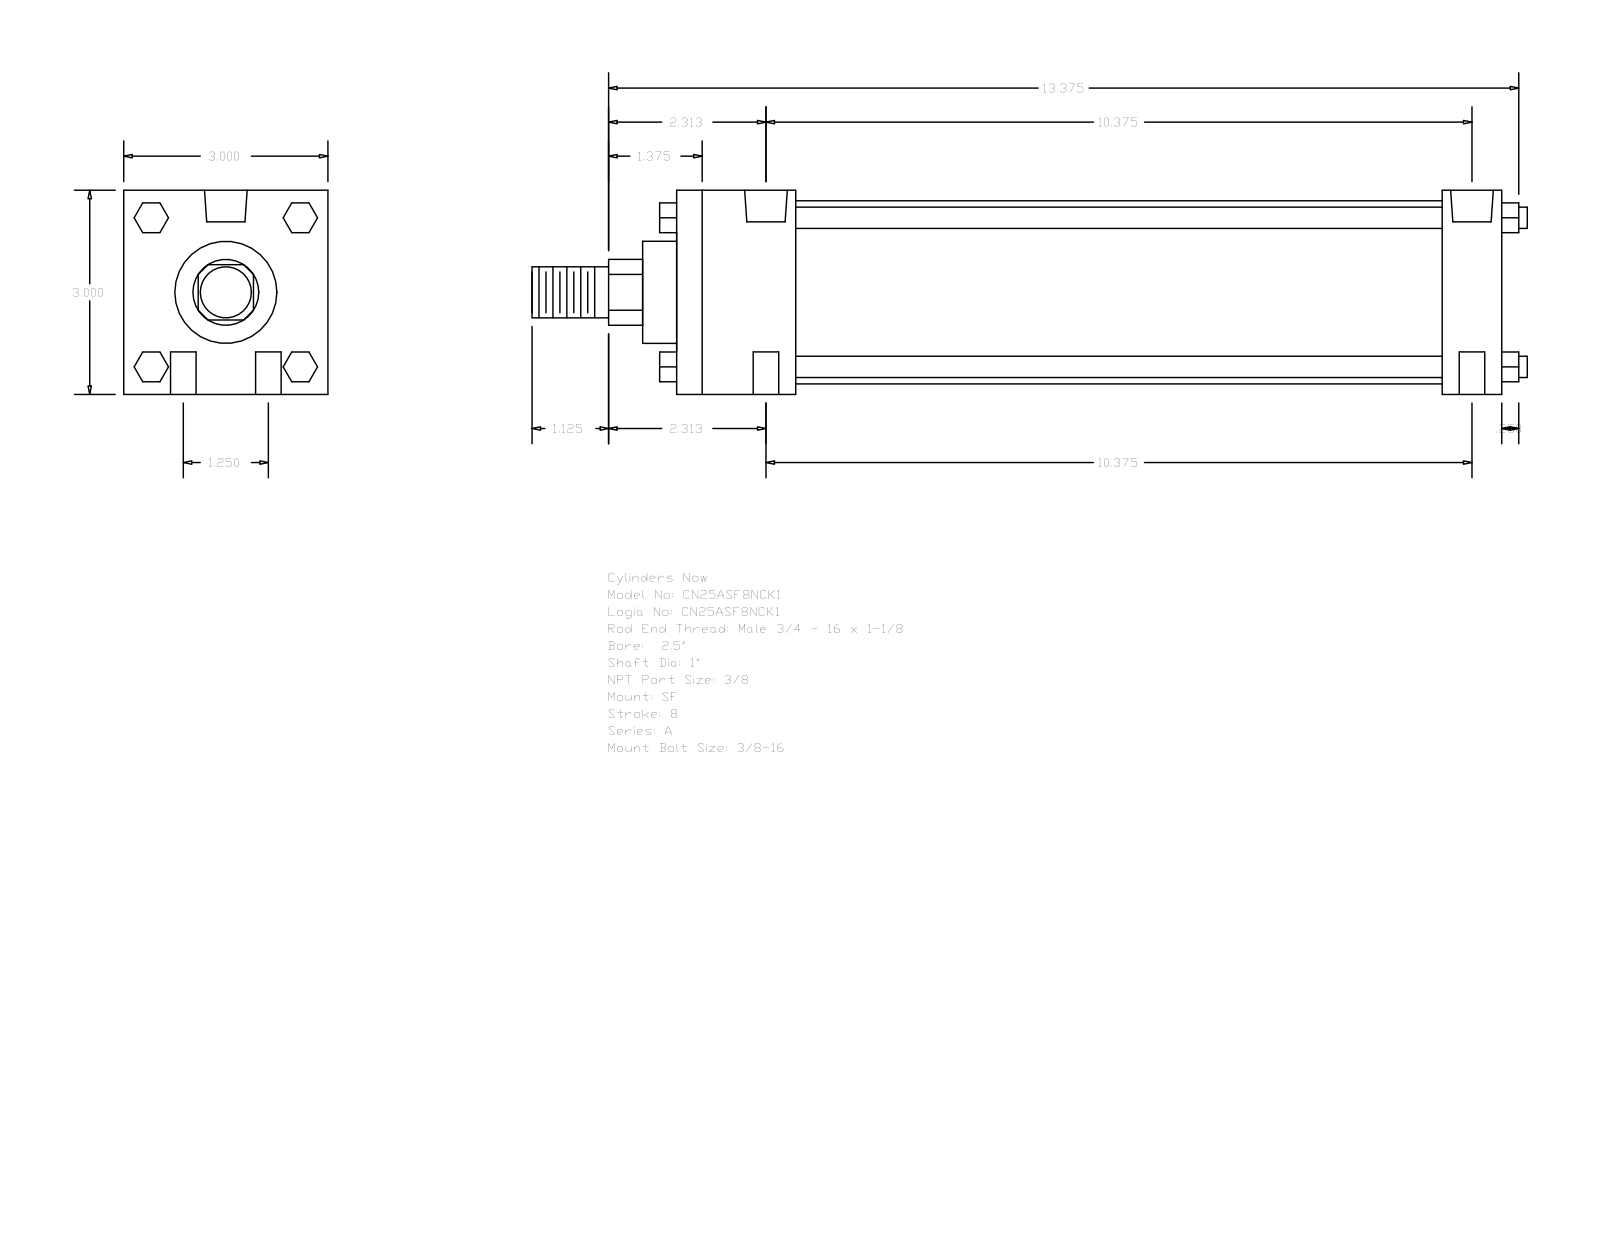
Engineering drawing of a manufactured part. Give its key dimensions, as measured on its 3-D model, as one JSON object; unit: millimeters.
{"part_name": "A_SF__0250_1", "step_written_by": "GSSL Pune (CONFIG_CONTROL_DESIGN)", "units": "millimeters", "bodies": {"solids": 0, "faces": 124, "planar": 94, "cylindrical": 30, "other": 0}, "overall_size": [371.48, 76.2, 76.2], "round_holes": [[9.53, 4], [5.56, 2], [15.93, 2]], "round_bosses_or_shafts": [[7.94, 4], [68.33, 1], [38.1, 1], [25.4, 1], [19.05, 1]], "partial_cylinders_radius": [[12.29, 1]], "face_to_face_distances": [76.2, 307.98, 285.75, 22.23, 44.45, 241.3, 263.53, 12.7, 320.68, 6.35], "hole_center_spacings": [15.88, 264, 263.52, 31.76, 265.43, 268.28]}
